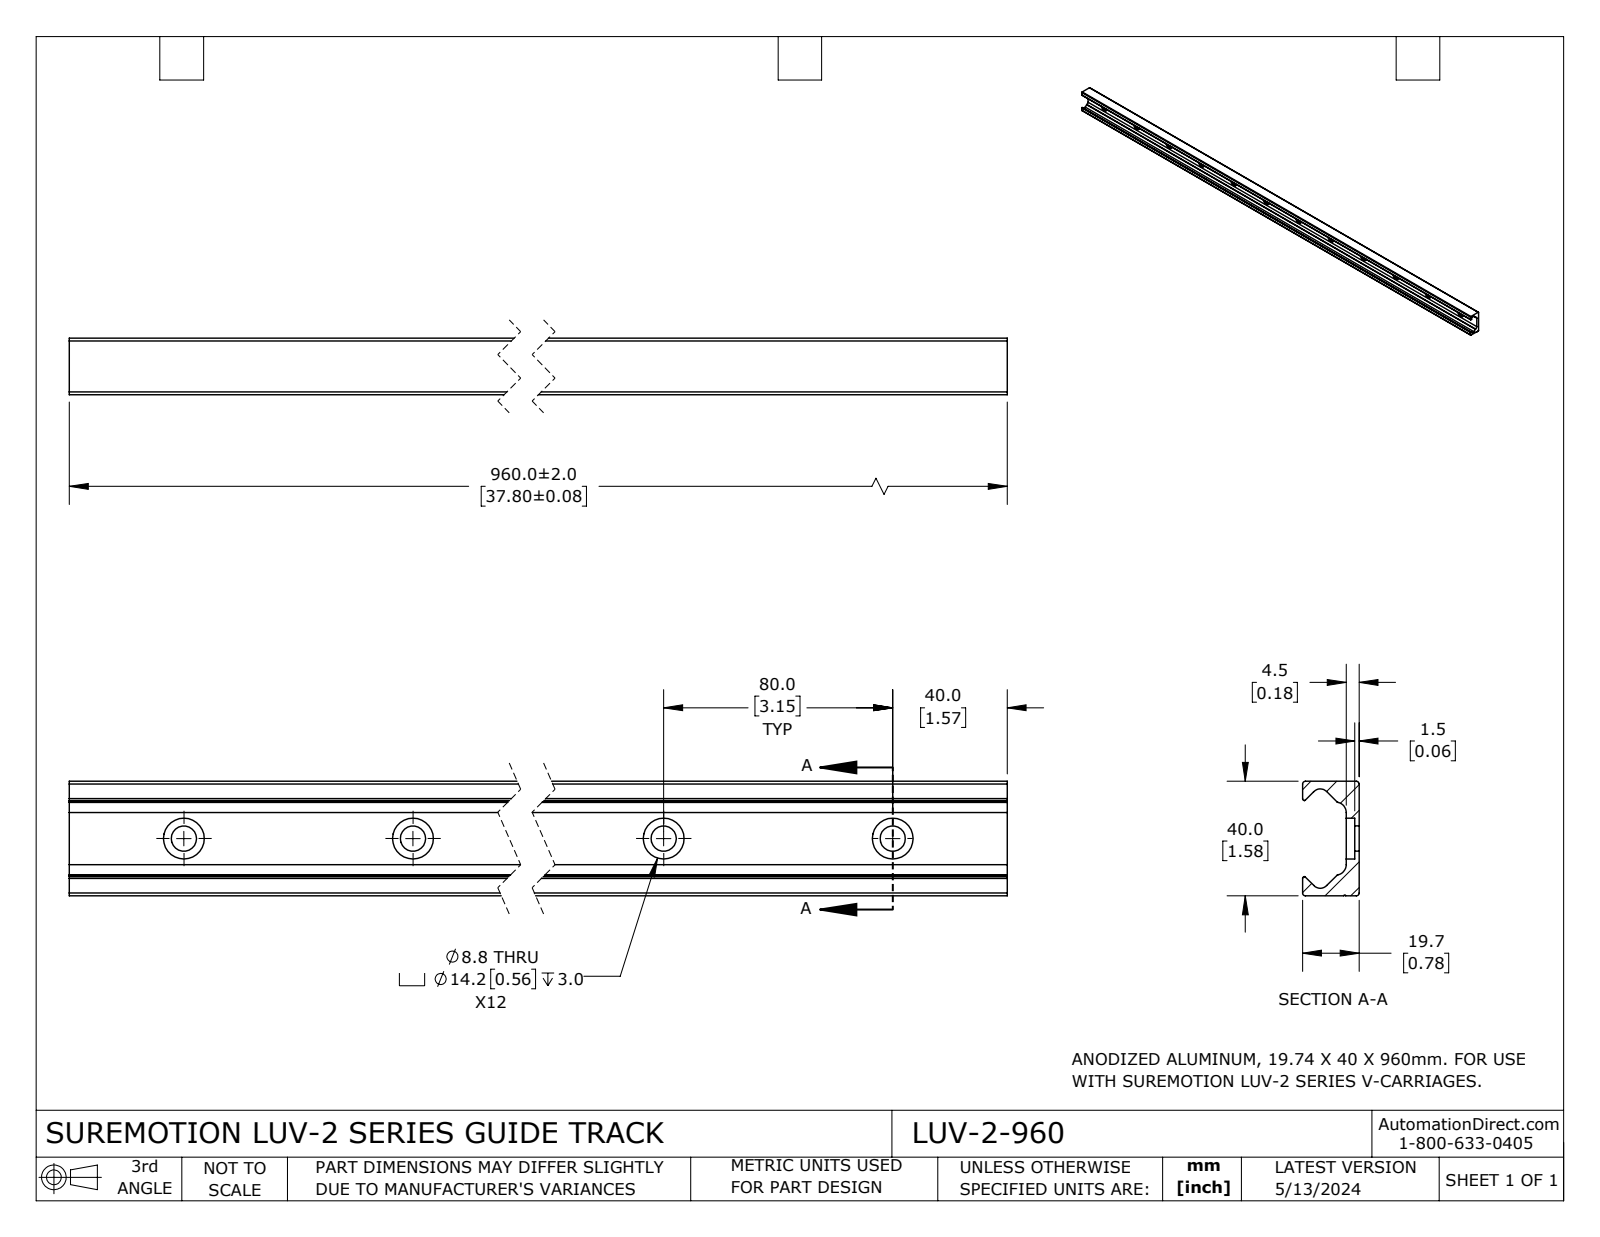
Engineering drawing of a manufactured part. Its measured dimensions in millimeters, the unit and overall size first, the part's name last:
Units: millimetres
Overall size (bounding box): 960 × 40.01 × 19.74
Round holes (diameter × count): ⌀8.81 ×12, ⌀14.25 ×12
Partial cylindrical surfaces — rounded edges, fillets, slot ends (radius × count): R0.99 ×4, R0.43 ×2, R0.64 ×2, R0.64 ×2, R3.18 ×2, R3.61 ×2, R0.33 ×1
Main face-to-face distances: 40.02, 4.5, 19.74, 15.24, 26.37, 1.5, 3, 18.24, 960
Hole centre spacings: 80, 160, 240, 320, 400, 480, 560, 640
Volume: 319 450 mm³ · Surface area: 145 779 mm²
Bodies: 1 solid, 88 faces (25 planar, 63 cylindrical, 0 other)
Part name (STEP PRODUCT): LUV-2-960
STEP written by: SolidWorks 2023 (CONFIG_CONTROL_DESIGN)
